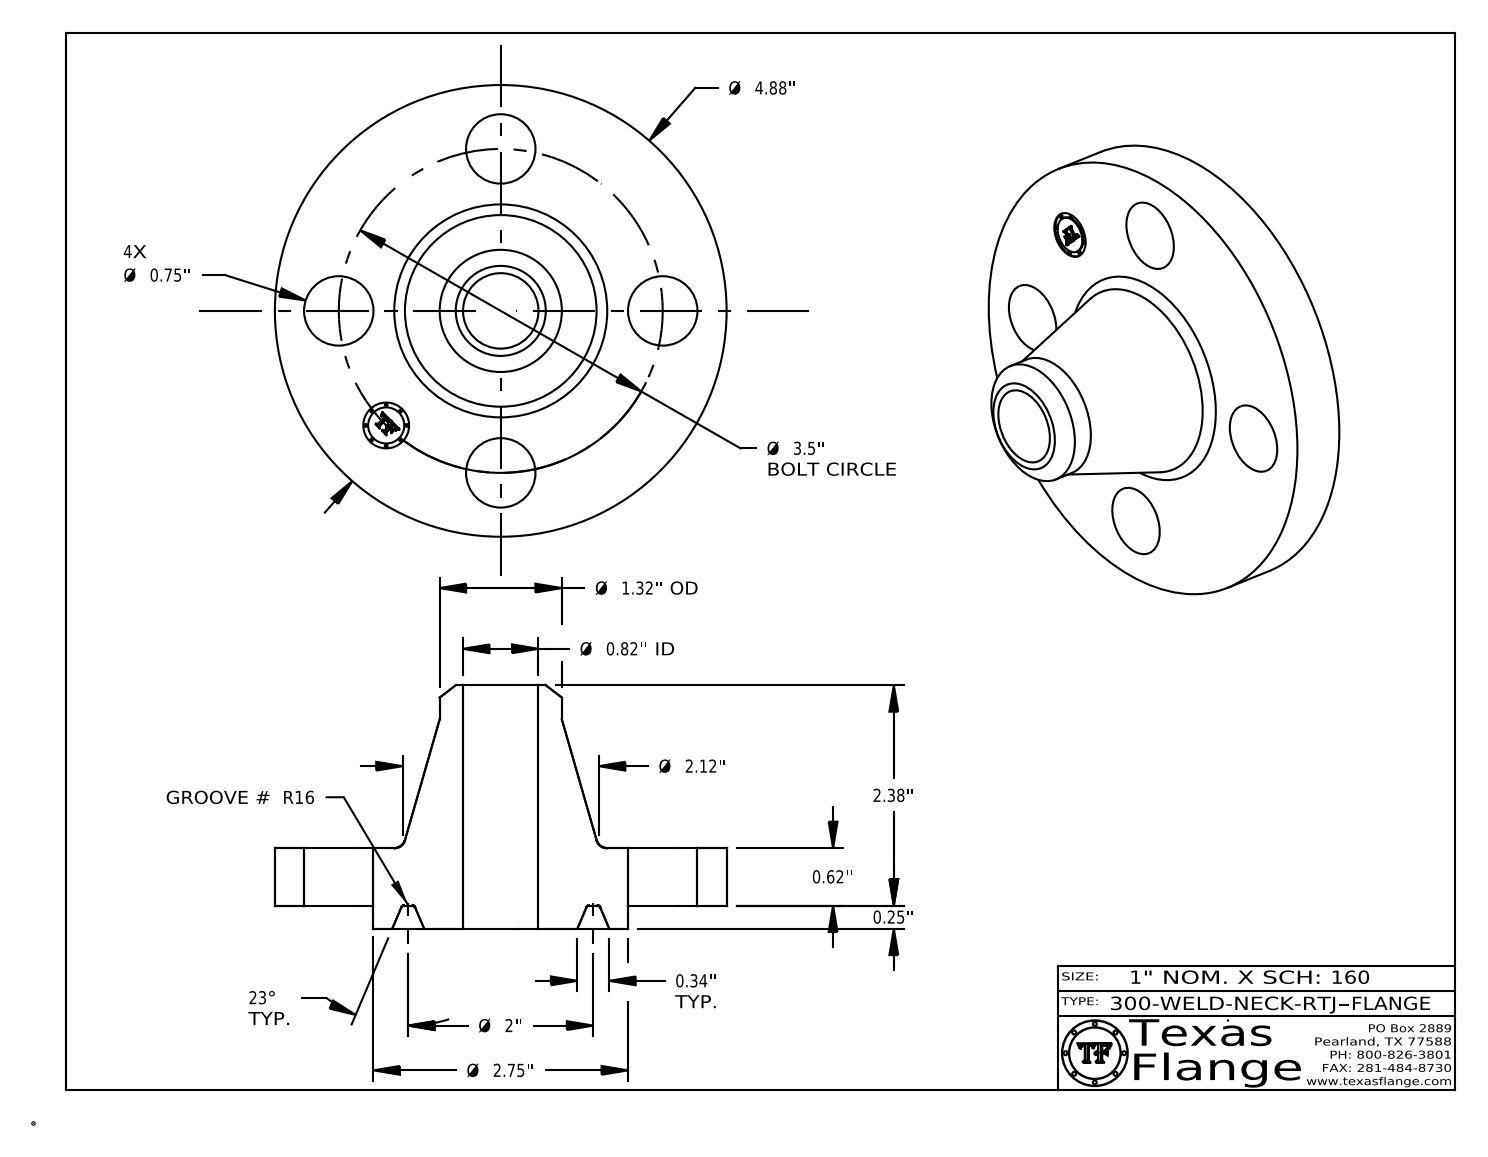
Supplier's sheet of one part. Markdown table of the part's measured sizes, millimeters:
| quantity | value |
| --- | --- |
| part name | 300-WELD-NECK-RTJ |
| STEP written by | CATIA V5 STEP AP214 (AUTOMOTIVE_DESIGN) |
| units | millimeters |
| bodies | 1 solid, 421 faces (371 planar, 36 cylindrical, 14 other) |
| overall size | 124 × 124 × 66.8 |
| volume | 229 400 mm³ |
| surface area | 42 460 mm² |
| round holes (diameter × count) | 19.1 × 4, 12.6 × 1, 20.7 × 1 |
| round bosses / shafts (diameter × count) | 0.8 × 8, 124 × 1, 69.9 × 1, 33.5 × 1, 9.9 × 1 |
| main face-to-face distances | 15.7, 6.4, 22.1, 66.8, 60.5, 44.7, 0.4, 21.7, 15.4, 45.1 |
| hole center spacings | 44.5, 62.9, 34, 82.1, 88.9 |
